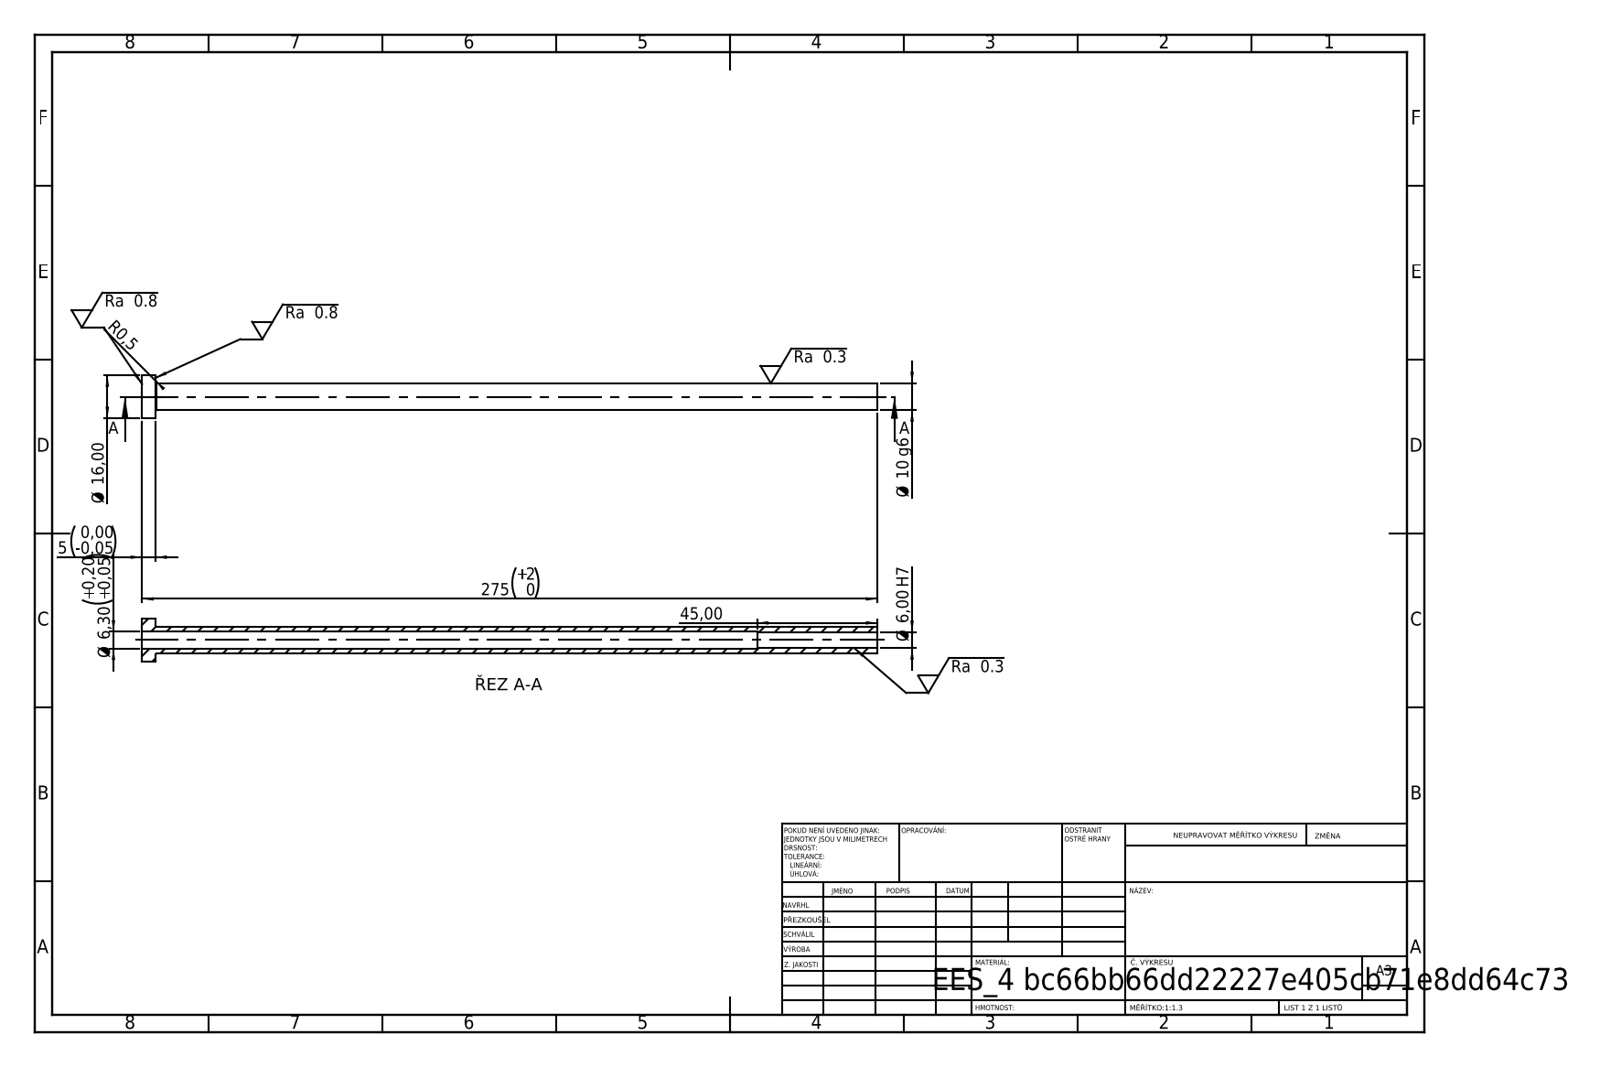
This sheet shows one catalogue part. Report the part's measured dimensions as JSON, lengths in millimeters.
{"step_written_by": "SolidWorks 2019 (CONFIG_CONTROL_DESIGN)", "units": "millimeters", "bodies": {"solids": 1, "faces": 14, "planar": 4, "cylindrical": 8, "other": 2}, "overall_size": [275, 16, 16], "volume_mm3": 13771, "surface_area_mm2": 14473, "round_holes": [[6, 1], [6.3, 1]], "round_bosses_or_shafts": [[16, 1], [10, 1]], "face_to_face_distances": [5, 275, 270, 230, 225, 45]}
